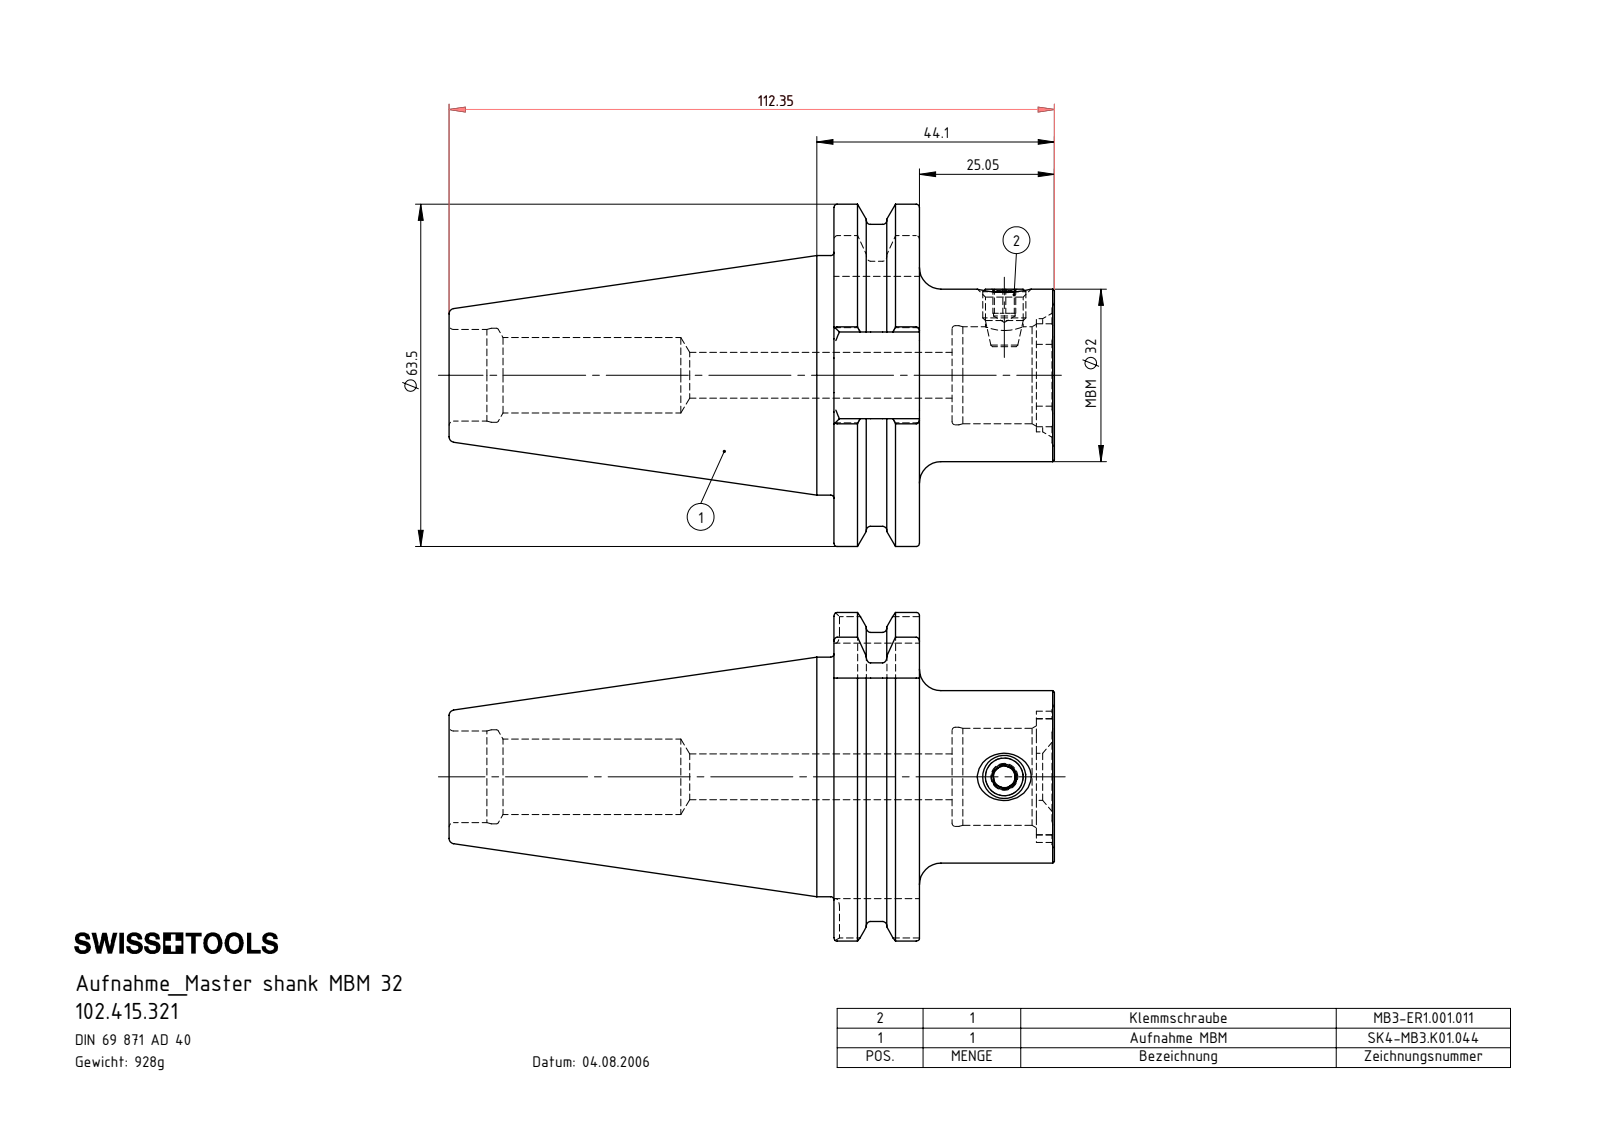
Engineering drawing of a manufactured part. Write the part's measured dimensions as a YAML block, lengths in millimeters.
part_name: "102.415.321; SK4-MB3.K01.044_C; MB3-ER1.001.011_A"
step_written_by: "SolidWorks 2017 (CONFIG_CONTROL_DESIGN)"
units: millimeters
bodies: {solids: 2, faces: 171, planar: 55, cylindrical: 50, other: 66}
overall_size: [112.35, 63.5, 60.94]
volume: 118267
surface_area: 23515
round_holes:
  - {diameter: 4, count: 1}
  - {diameter: 7, count: 1}
  - {diameter: 8.5, count: 1}
  - {diameter: 14, count: 1}
  - {diameter: 17, count: 1}
  - {diameter: 17.45, count: 1}
  - {diameter: 18, count: 1}
  - {diameter: 18.4, count: 1}
round_bosses_or_shafts:
  - {diameter: 44.45, count: 1}
  - {diameter: 32, count: 1}
  - {diameter: 8, count: 1}
partial_cylinders:
  - {radius: 1.6, count: 8}
  - {radius: 3.2, count: 4}
  - {radius: 10.5, count: 1}
  - {radius: 12.18, count: 1}
  - {radius: 28, count: 1}
  - {radius: 31.75, count: 1}
face_to_face_distances: [15.85, 47.4, 40.9, 25.05, 21.9, 6.05, 19, 37.55, 21.7, 15.65]
